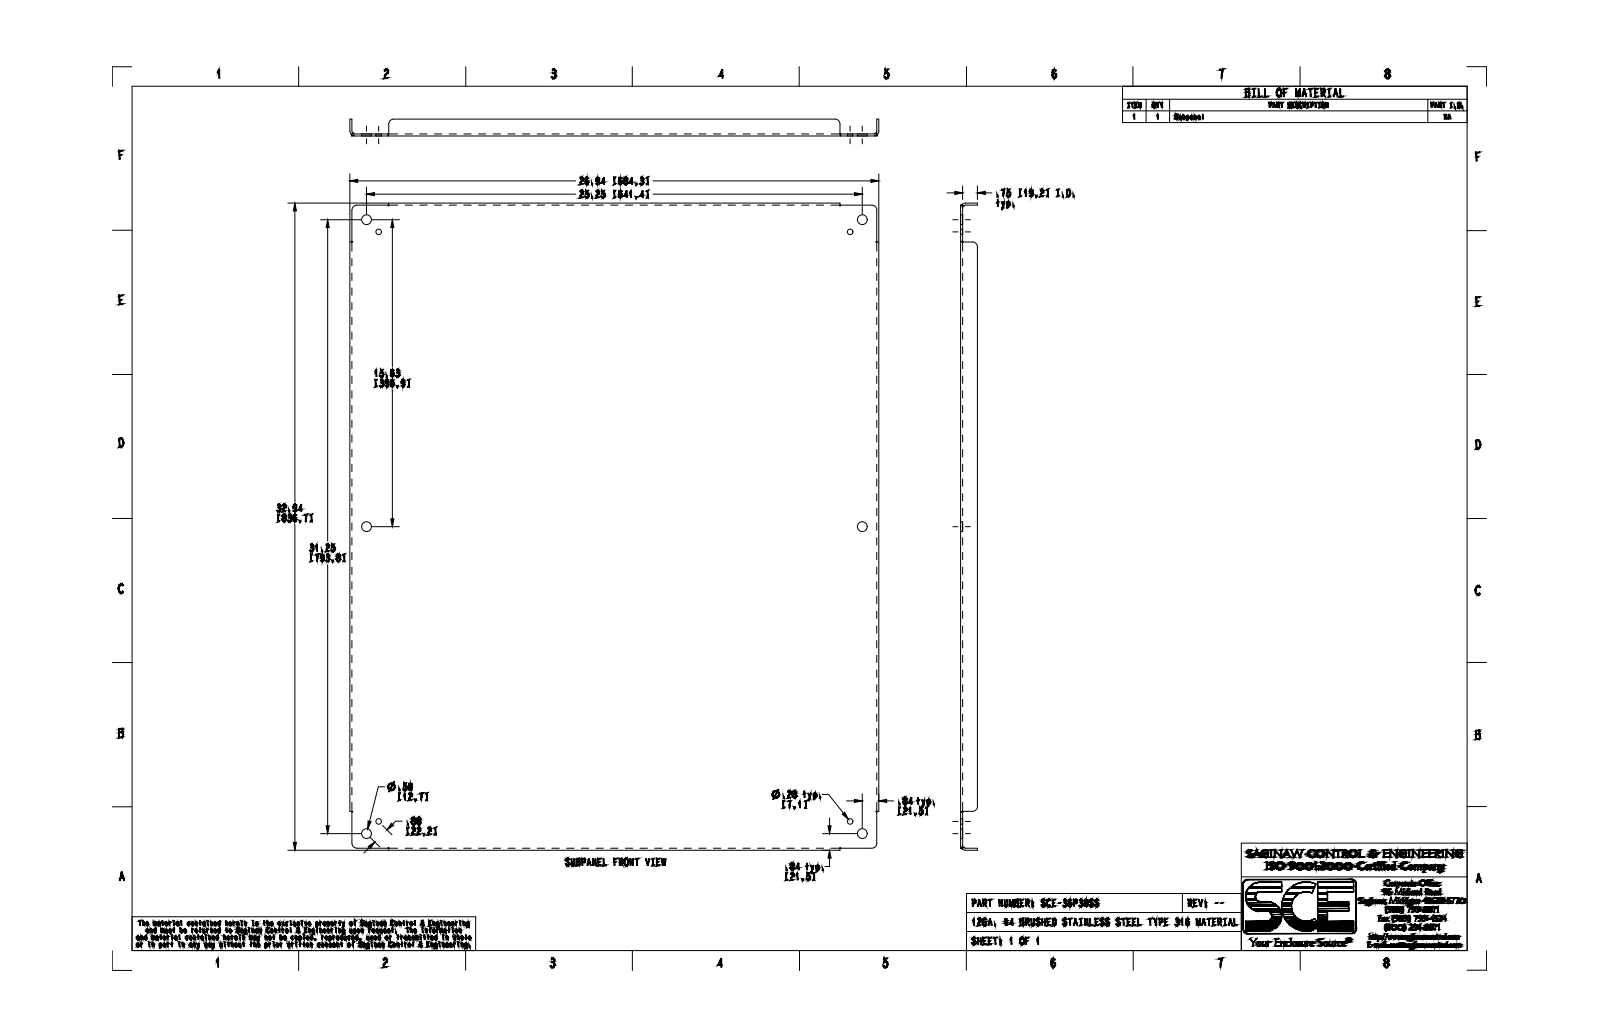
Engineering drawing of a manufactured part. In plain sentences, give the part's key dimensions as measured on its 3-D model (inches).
The part is named "SCE-36P30SS". Its 3-D file was written by "SolidWorks 2019 (CONFIG_CONTROL_DESIGN)". It is 1 solid with 84 faces: 30 planar, 30 cylindrical and 24 other. Overall it measures 32.941 by 26.941 by 0.858 inches. Its volume is 99.22 cubic inches and its surface area 1 922 square inches. Round holes: 6 of diameter 0.5, 4 of diameter 0.281. Partial cylindrical surfaces (rounded edges, fillets, slot ends): 8 of radius 0.25, 4 of radius 0.246, 2 of radius 0.142, 2 of radius 0.143. The main face-to-face distances are 0.104, 26.838, 32.838, 26.734, 26.942, 32.734, 32.942, 0.754, 0.858, 1.979. The hole center spacings are 0.875, 15.02, 15.626, 24.641, 28.844, 29.696, 30.639, 39.309.
